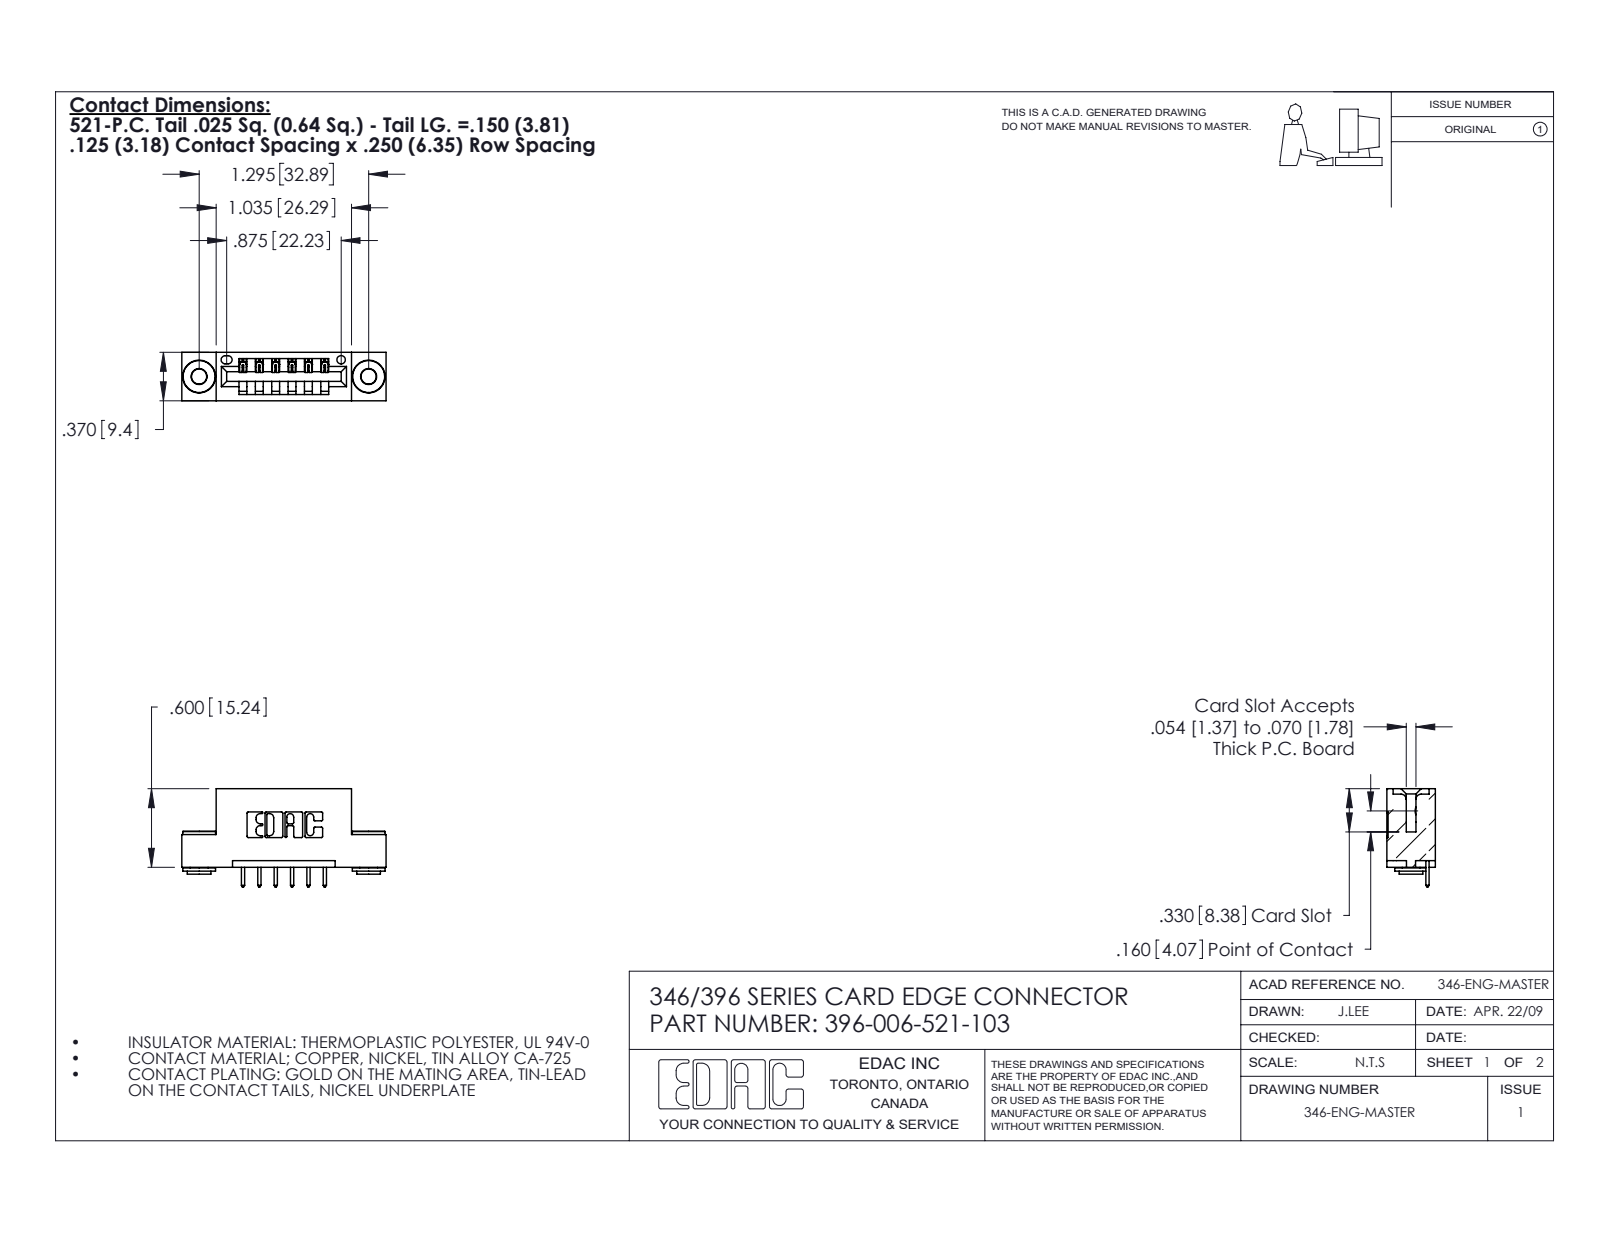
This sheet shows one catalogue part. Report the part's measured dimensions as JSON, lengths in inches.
{"part_name": "345-292-001_345-293-121; 396-006-521-103; 345-250-002_345-250-002-102; 346 Part_Flush Mounting Lugs - 0.156 Dia-TH", "step_written_by": "SolidWorks 2020 (CONFIG_CONTROL_DESIGN)", "units": "inches", "bodies": {"solids": 9, "faces": 522, "planar": 340, "cylindrical": 174, "other": 8}, "overall_size": [1.56, 0.75, 0.37], "volume_in3": 0.215, "surface_area_in2": 6.519, "round_holes": [[0.116, 2], [0.156, 2], [0.064, 1]], "round_bosses_or_shafts": [[0.25, 2], [0.18, 2], [0.136, 2]], "partial_cylinders_radius": [[0.01, 22], [0.006, 12], [0.01, 12], [0.007, 6], [0.031, 6], [0.026, 3], [0.031, 2], [0.04, 2]], "face_to_face_distances": [0.25, 0.37, 0.048, 0.322, 0.025, 0.148, 0.222, 0.1, 0.174, 0.125], "hole_center_spacings": [0.246, 1.092, 1.295]}
